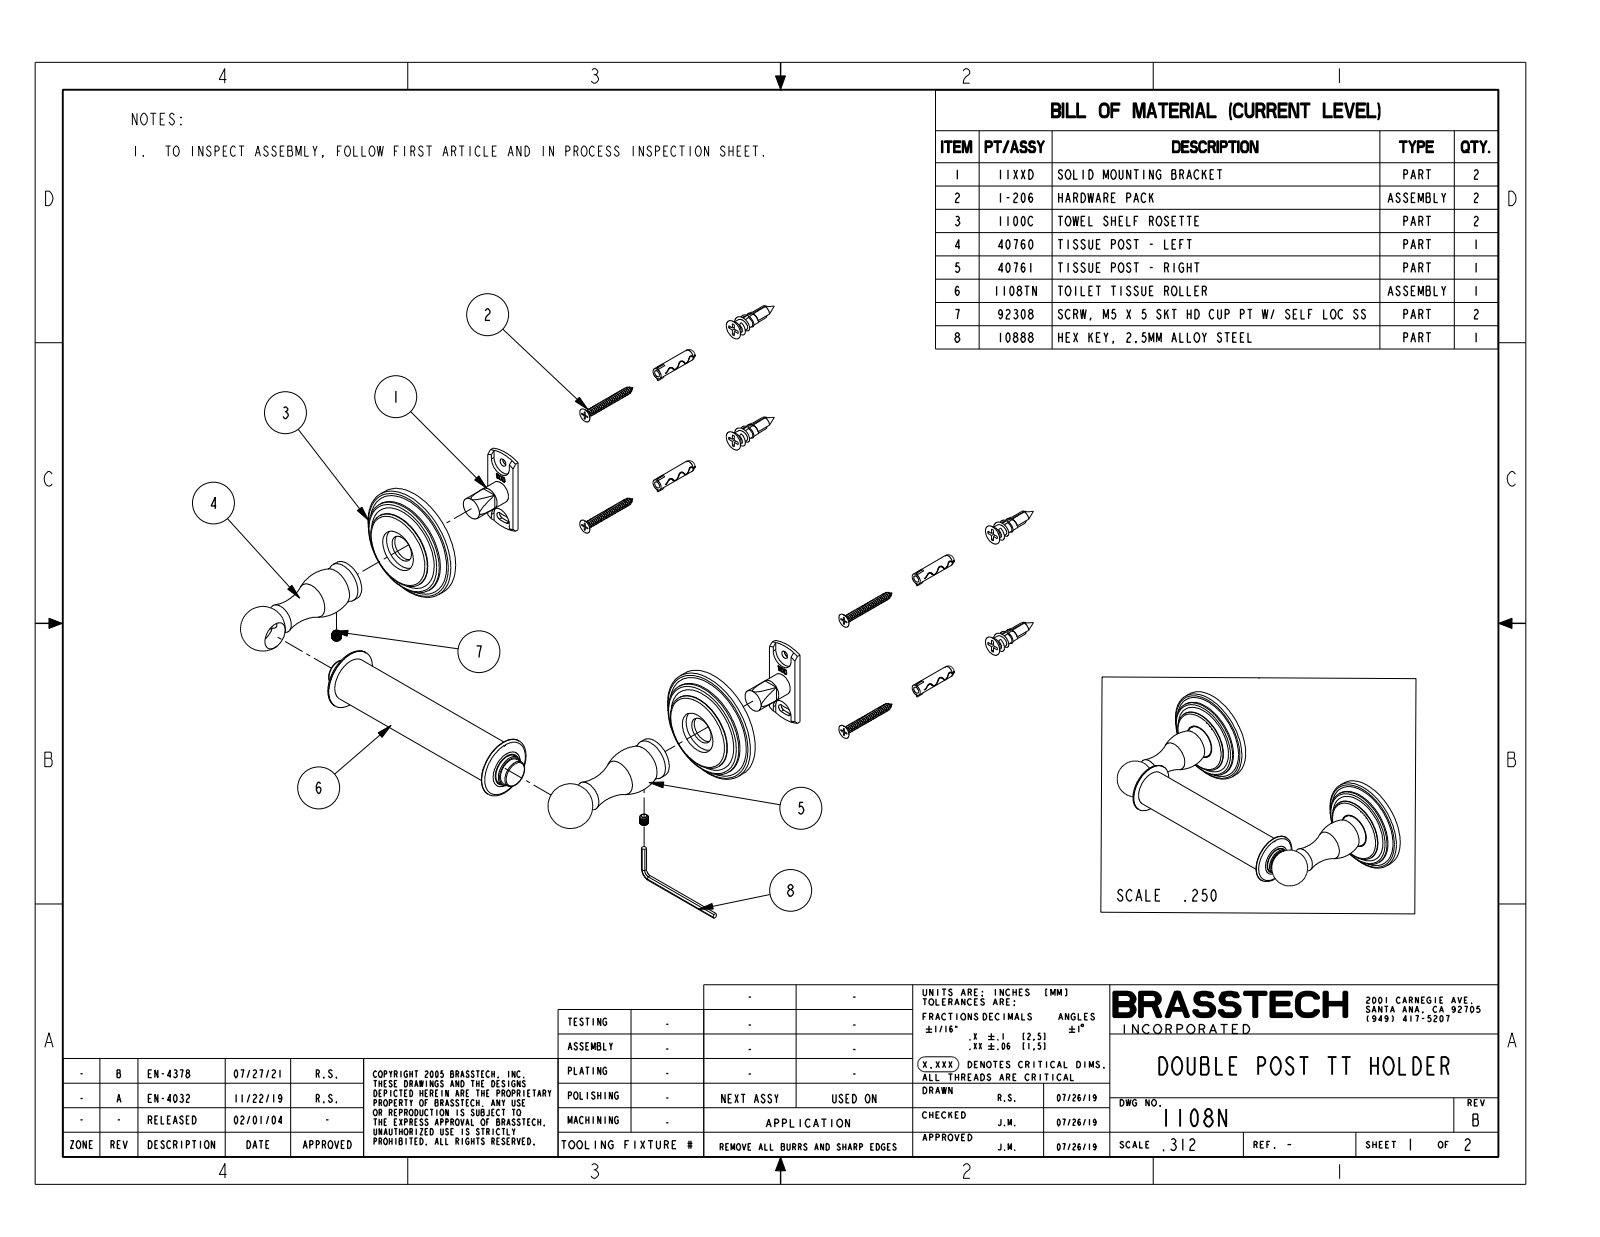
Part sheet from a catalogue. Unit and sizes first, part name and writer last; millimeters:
Units: millimetres
Overall size (bounding box): 217.4 × 93.8 × 65
Round holes (diameter × count): ⌀16 ×1, ⌀18 ×1
Round bosses / shafts (diameter × count): ⌀65 ×2, ⌀55.4 ×2, ⌀44.4 ×2, ⌀34.5 ×1, ⌀34.5 ×1, ⌀25 ×1, ⌀17.8 ×1, ⌀17.6 ×1
Main face-to-face distances: 13, 9.2, 3.8, 4.8, 4.4, 8.2, 120.7, 15.9, 136.5, 152.4
Volume: 175 300 mm³ · Surface area: 40 420 mm²
Bodies: 3 solids, 113 faces (19 planar, 32 cylindrical, 62 other)
Part name (STEP PRODUCT): 1108N
STEP written by: CREO PARAMETRIC BY PTC INC, 2018400 (AUTOMOTIVE_DESIGN)
